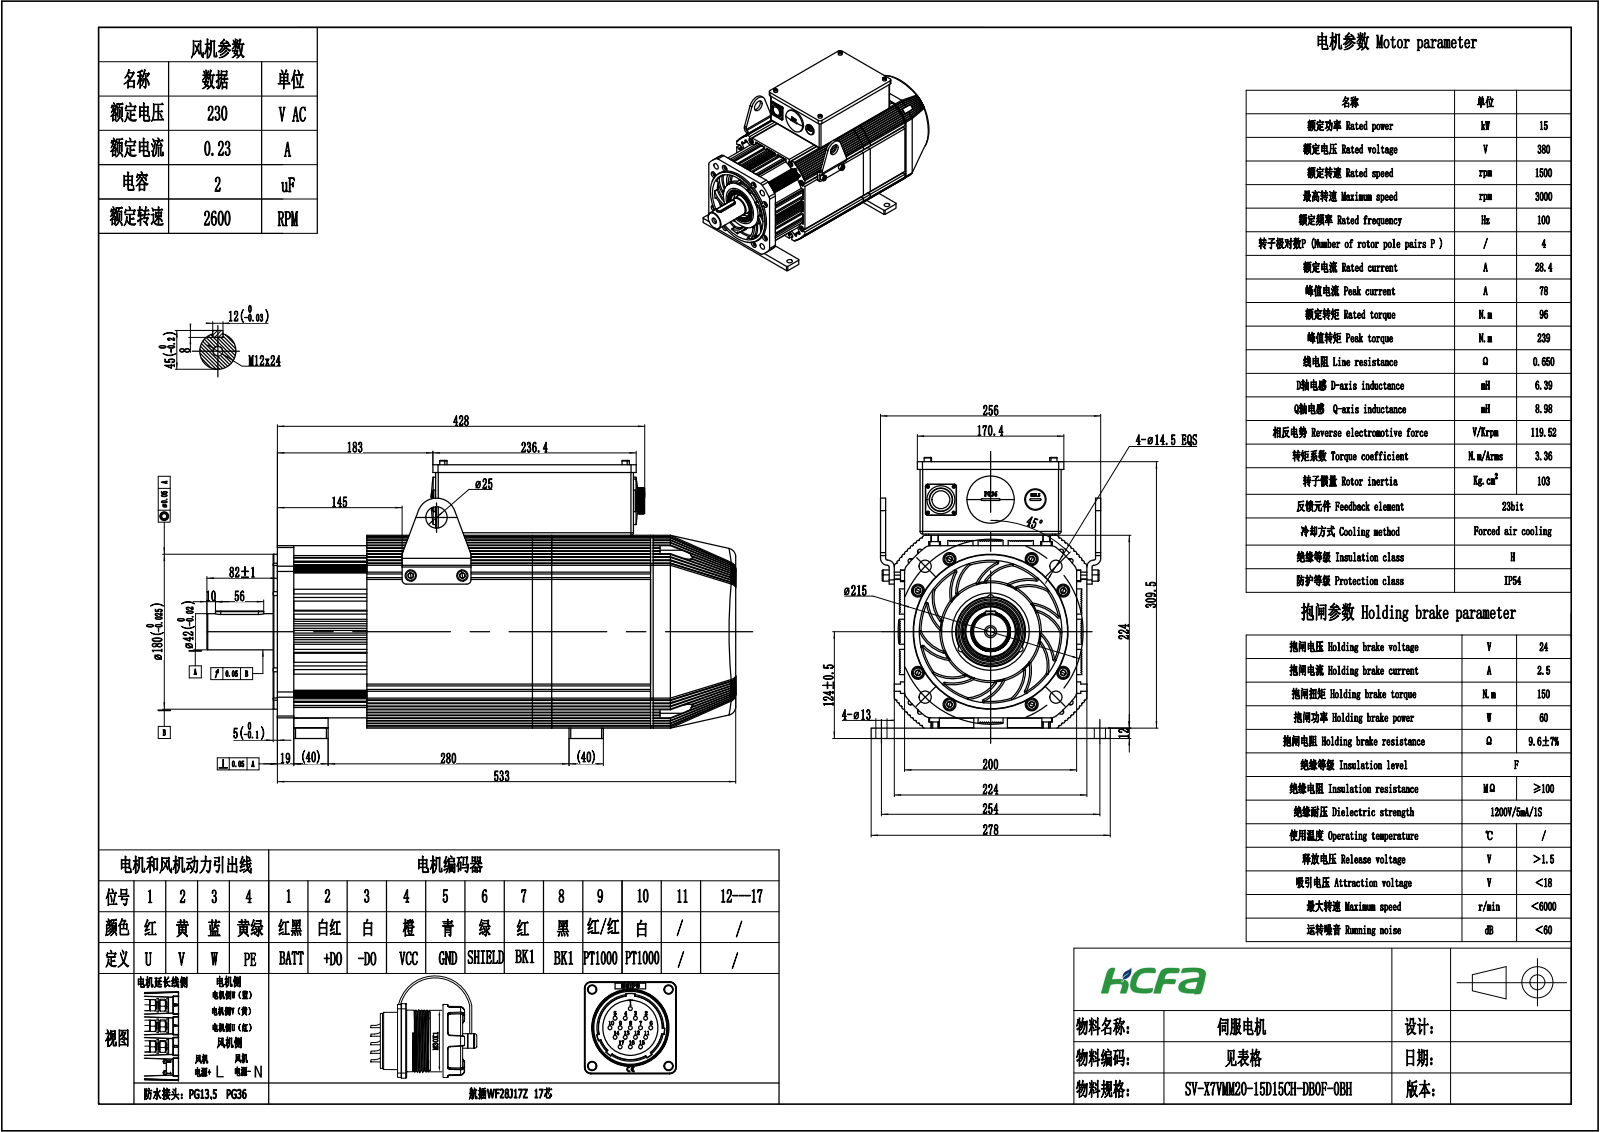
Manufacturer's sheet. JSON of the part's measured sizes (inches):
{"part_name": "10002030101-0036-SV-X7VMM20-15D15CH-DB0F-0BH-4段外形图", "step_written_by": "SolidWorks 2021 (CONFIG_CONTROL_DESIGN)", "units": "inches", "bodies": {"solids": 8, "faces": 3834, "planar": 1629, "cylindrical": 1202, "other": 1003}, "overall_size": [24.209, 12.854, 10.945], "volume_in3": 1432, "surface_area_in2": 1772, "round_holes": [[0.354, 24], [0.591, 14], [0.512, 8], [0.394, 6], [0.098, 4], [0.126, 4], [0.228, 4], [0.268, 4], [0.276, 4], [0.571, 4], [0.402, 1], [0.669, 1]], "round_bosses_or_shafts": [[0.059, 17], [0.512, 10], [0.315, 10], [0.335, 4], [0.197, 4], [1.575, 2], [7.087, 1], [4.953, 1]], "partial_cylinders_radius": [[0.079, 112], [0.039, 26], [0.059, 20], [0.197, 18], [0.055, 16], [0.118, 12], [0.008, 10], [0.394, 10]], "face_to_face_distances": [8.819, 0.079, 12.106, 0.472, 0.236, 12.185, 1.181, 7.638, 1.26, 7.559], "hole_center_spacings": [1.16, 1.7, 3.819, 4.885, 5.401, 5.449, 6.413, 6.581]}
